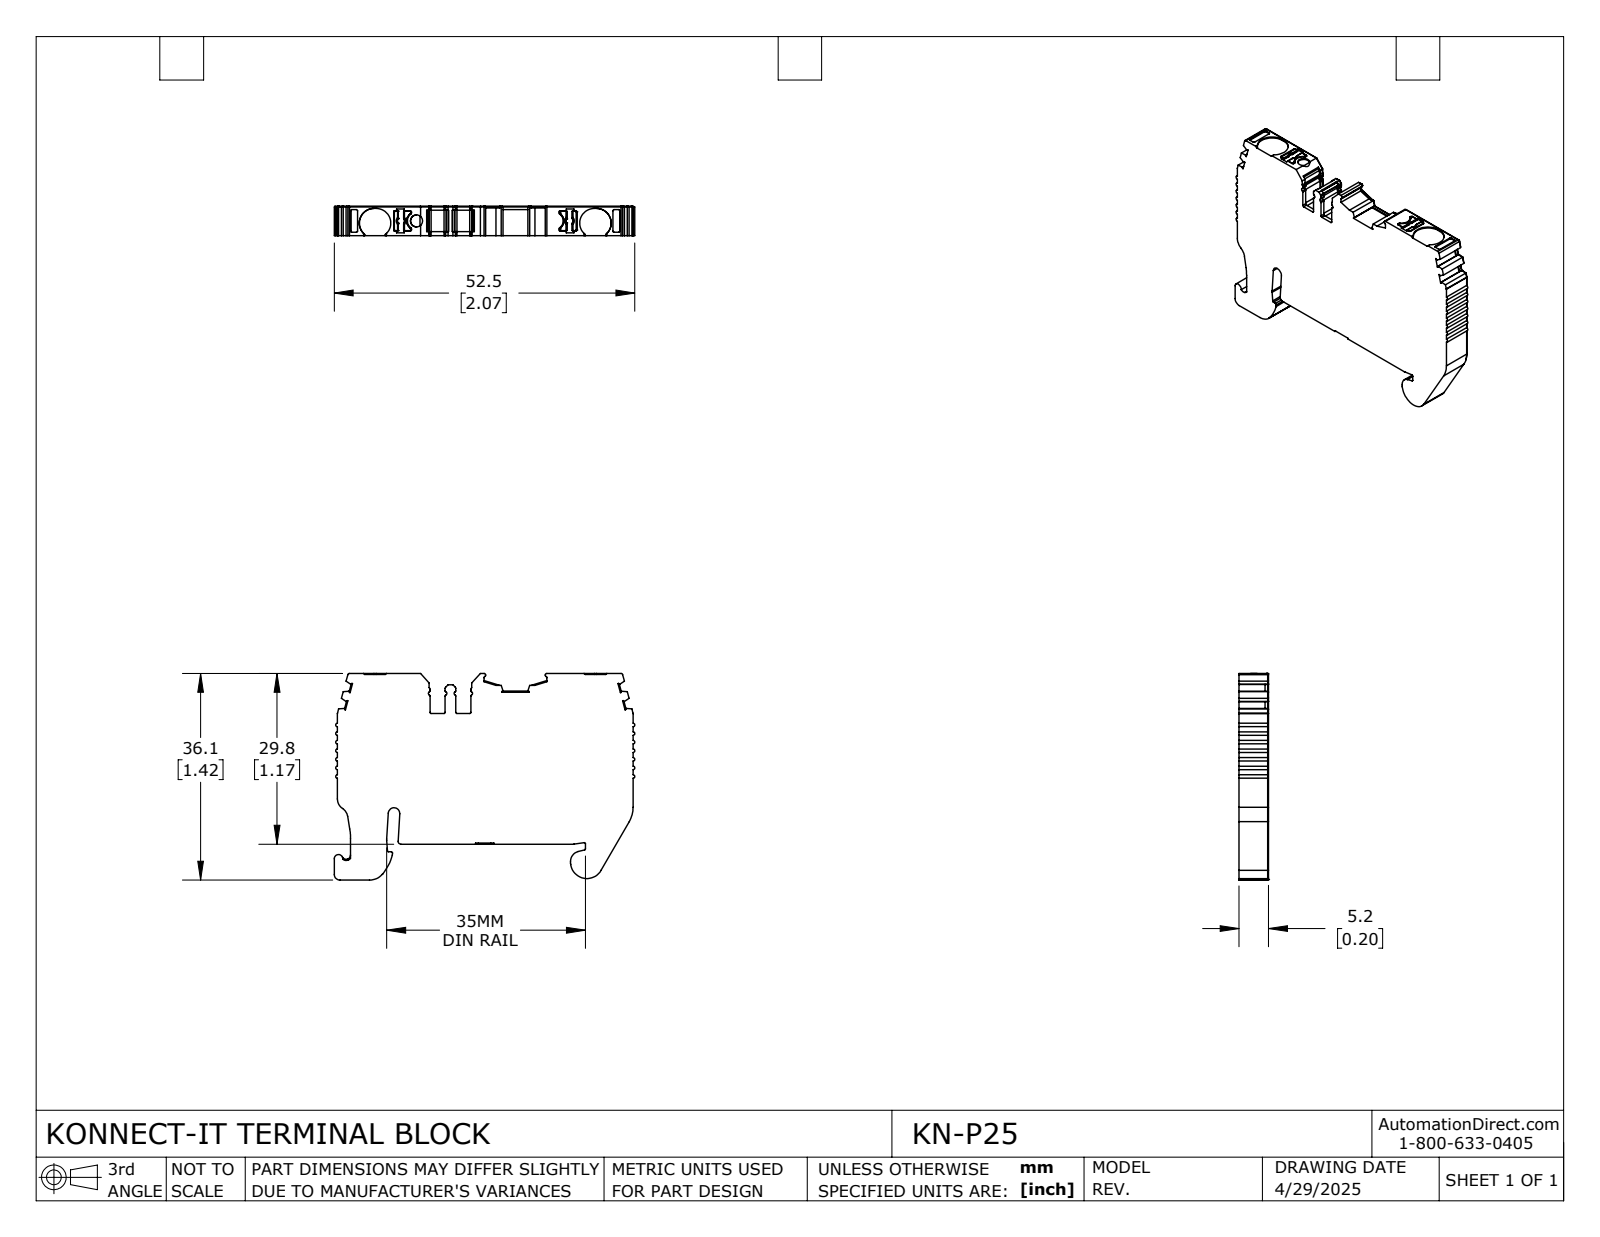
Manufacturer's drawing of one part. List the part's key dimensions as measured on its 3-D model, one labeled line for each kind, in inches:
Part name (STEP PRODUCT): KN-P25
STEP written by: SolidWorks 2024 (CONFIG_CONTROL_DESIGN)
Units: inches
Bodies: 1 solid, 584 faces (308 planar, 239 cylindrical, 37 other)
Overall size (bounding box): 2.066 × 1.42 × 0.203
Volume: 0.468 in³ · Surface area: 6.63 in²
Round holes (diameter × count): ⌀0.083 ×1
Partial cylindrical surfaces — rounded edges, fillets, slot ends (radius × count): R0.008 ×54, R0.012 ×39, R0.02 ×18, R0.004 ×17, R0.016 ×9, R0.006 ×8, R0.1 ×4, R0.039 ×3
Main face-to-face distances: 0.203, 1.166, 1.174, 2.033, 0.177, 0.197, 0.246, 1.412, 0.079, 1.42
